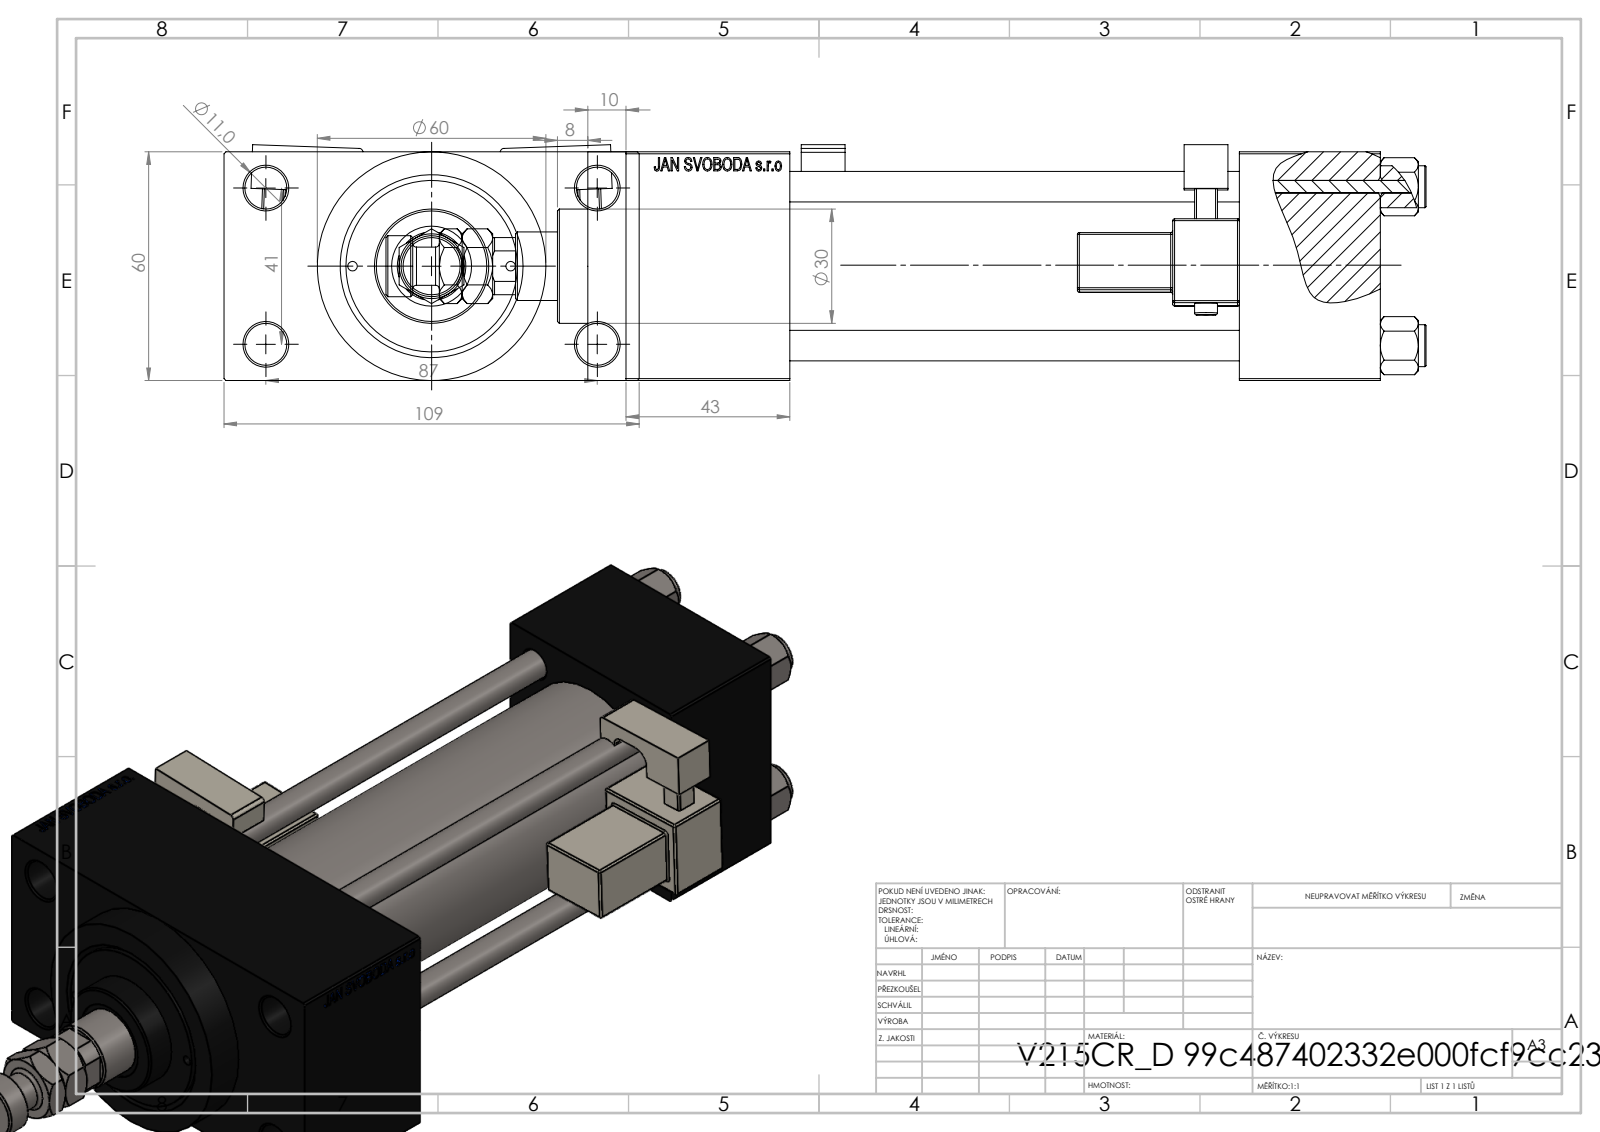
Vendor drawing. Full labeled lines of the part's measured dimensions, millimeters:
Part name (STEP PRODUCT): V215_VC_A; V215CR_VCP_D; V215CR_D_Body; V215CR_D_TYCINKA (+3 more)
STEP written by: SolidWorks 2019 (CONFIG_CONTROL_DESIGN)
Units: millimetres
Bodies: 14 solids, 1318 faces (574 planar, 156 cylindrical, 588 other)
Overall size (bounding box): 273 × 109 × 61.9
Volume: 610 221 mm³ · Surface area: 162 291 mm²
Round holes (diameter × count): ⌀8 ×4, ⌀11 ×4, ⌀2.5 ×2, ⌀7 ×2, ⌀16.66 ×2, ⌀24 ×2, ⌀8.5 ×1, ⌀18 ×1, ⌀21 ×1, ⌀31 ×1, ⌀40 ×1, ⌀45 ×1
Round bosses / shafts (diameter × count): ⌀11 ×4, ⌀6 ×2, ⌀60 ×1, ⌀46 ×1, ⌀30 ×1, ⌀16 ×1, ⌀10 ×1
Partial cylindrical surfaces — rounded edges, fillets, slot ends (radius × count): R0.5 ×48, R1 ×2, R2.5 ×2, R4 ×2, R8.5 ×1
Main face-to-face distances: 60, 118, 24.5, 84.5, 37, 155, 198, 161, 43, 109
Hole centre spacings: 20.85, 22.65, 29.49, 30.62, 41.7, 46.53, 47.15, 48.09
